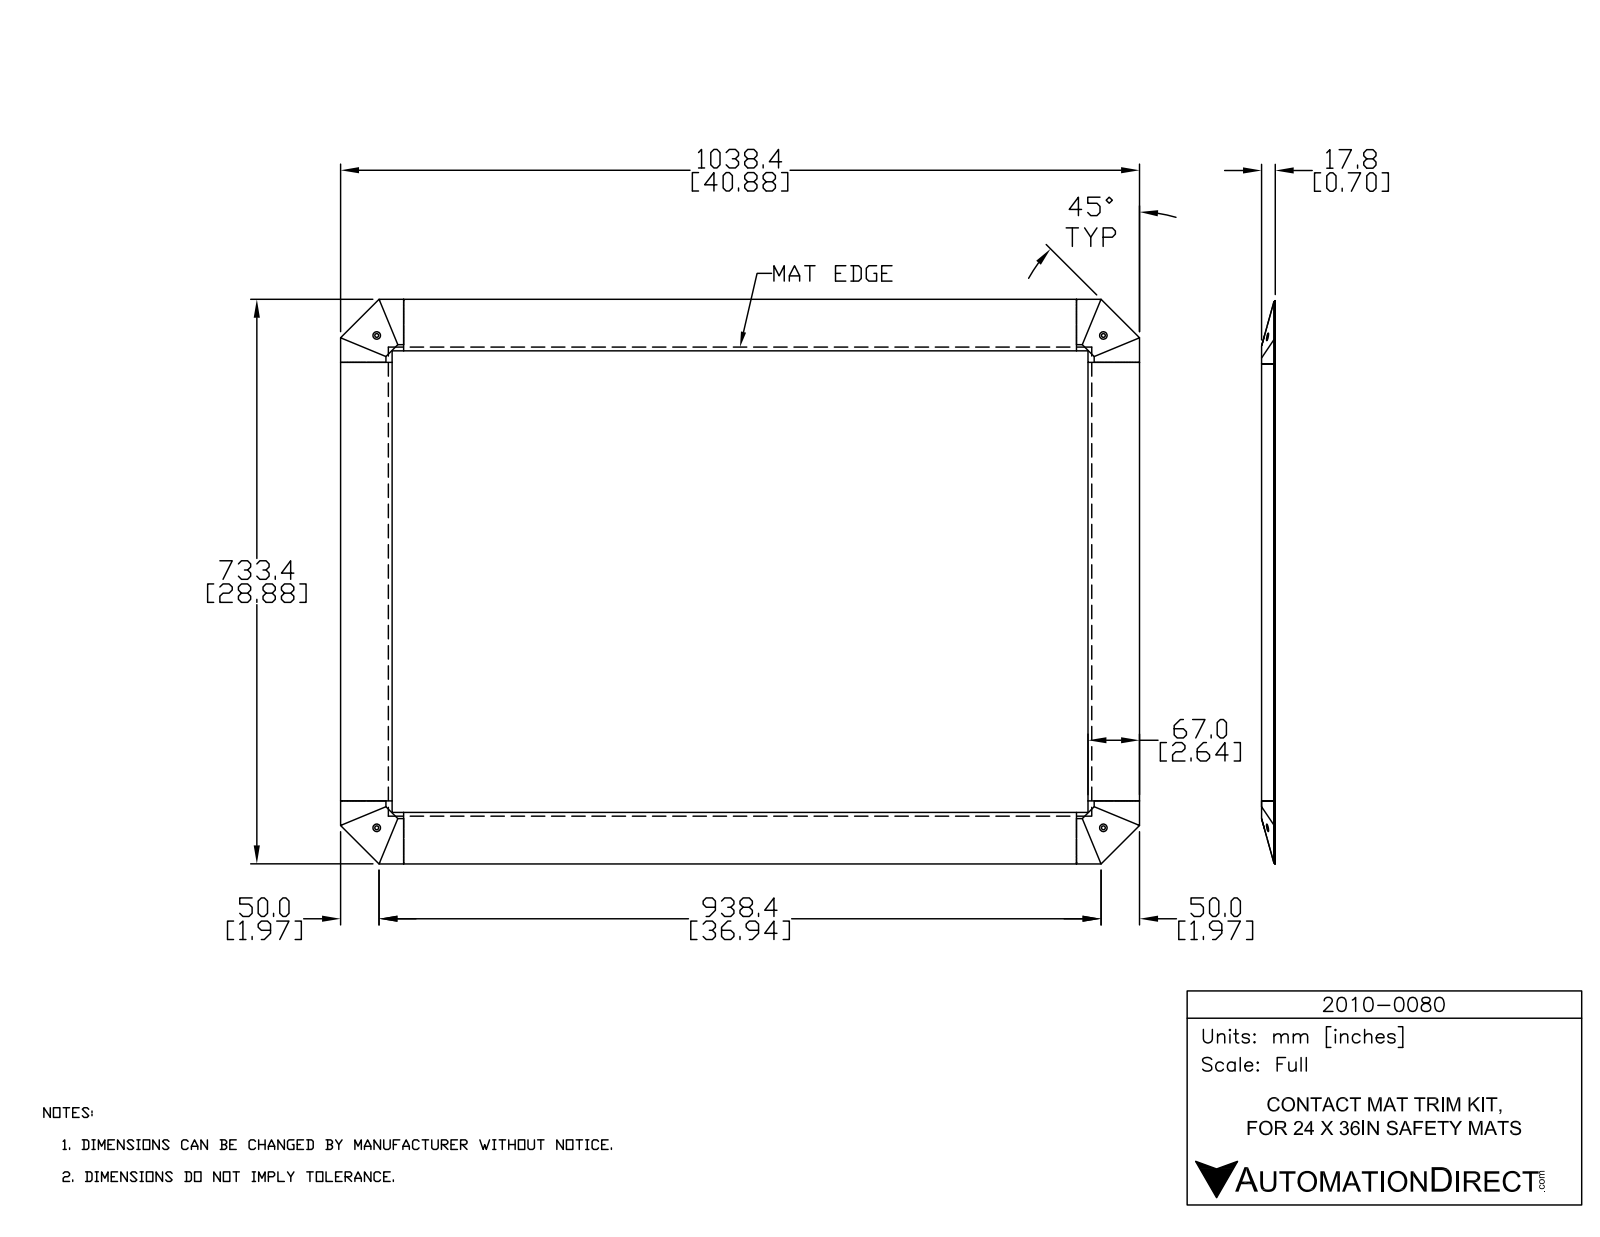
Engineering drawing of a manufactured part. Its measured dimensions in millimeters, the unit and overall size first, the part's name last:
Units: millimetres
Overall size (bounding box): 1038.4 × 733.6 × 17.8
Round holes (diameter × count): ⌀5 ×4, ⌀9.8 ×4
Round bosses / shafts (diameter × count): ⌀10 ×4
Partial cylindrical surfaces — rounded edges, fillets, slot ends (radius × count): R0.2 ×200, R1 ×108, R0.5 ×60, R0.4 ×8, R13 ×8, R7.4 ×4, R10 ×4
Main face-to-face distances: 2.9, 1.9, 3, 1, 4.8, 16, 2, 1, 3.9, 7.7
Hole centre spacings: 639.6, 944.4, 1140.6
Volume: 930 100 mm³ · Surface area: 721 900 mm²
Bodies: 1 solid, 2109 faces (1613 planar, 440 cylindrical, 56 other)
Part name (STEP PRODUCT): 2010-0080
STEP written by: SolidWorks 2018 (AUTOMOTIVE_DESIGN)
